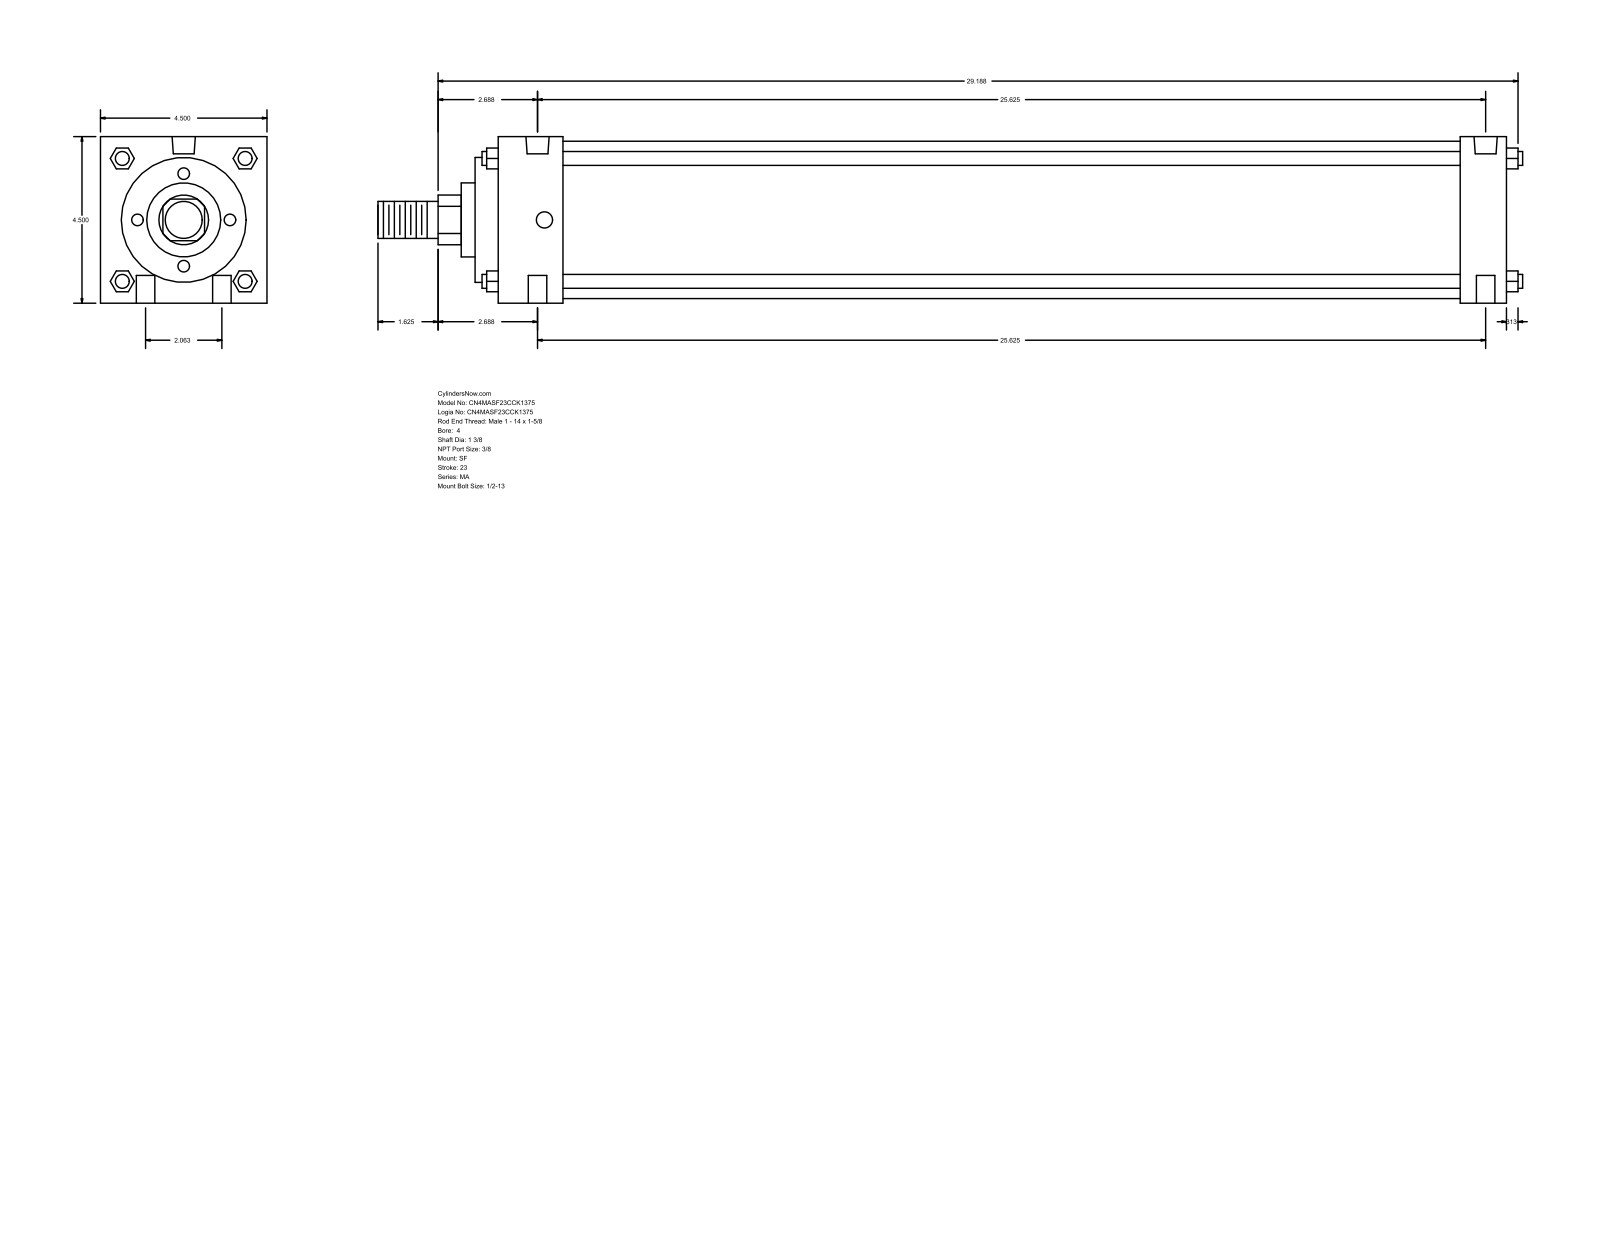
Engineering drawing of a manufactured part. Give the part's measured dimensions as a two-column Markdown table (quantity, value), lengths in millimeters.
| quantity | value |
| --- | --- |
| part name | MA_SF__0400_1.375 |
| STEP written by | GSSL Pune (CONFIG_CONTROL_DESIGN) |
| units | millimeters |
| bodies | 0 solids, 126 faces (95 planar, 31 cylindrical, 0 other) |
| overall size | 785.81 × 114.3 × 114.3 |
| round holes (diameter × count) | 12.7 × 4, 11.11 × 2, 15.93 × 2 |
| round bosses / shafts (diameter × count) | 9.53 × 4, 107.95 × 1, 85.72 × 1, 50.8 × 1, 34.92 × 1, 25.4 × 1 |
| partial cylindrical surfaces (radius × count) | 17.06 × 1 |
| main face-to-face distances | 114.3, 692.15, 708.02, 15.87, 676.27, 660.4, 31.75, 60.32, 44.45, 615.95 |
| hole center spacings | 26.19, 651.41, 650.88, 52.38, 652.98, 641.35 |
